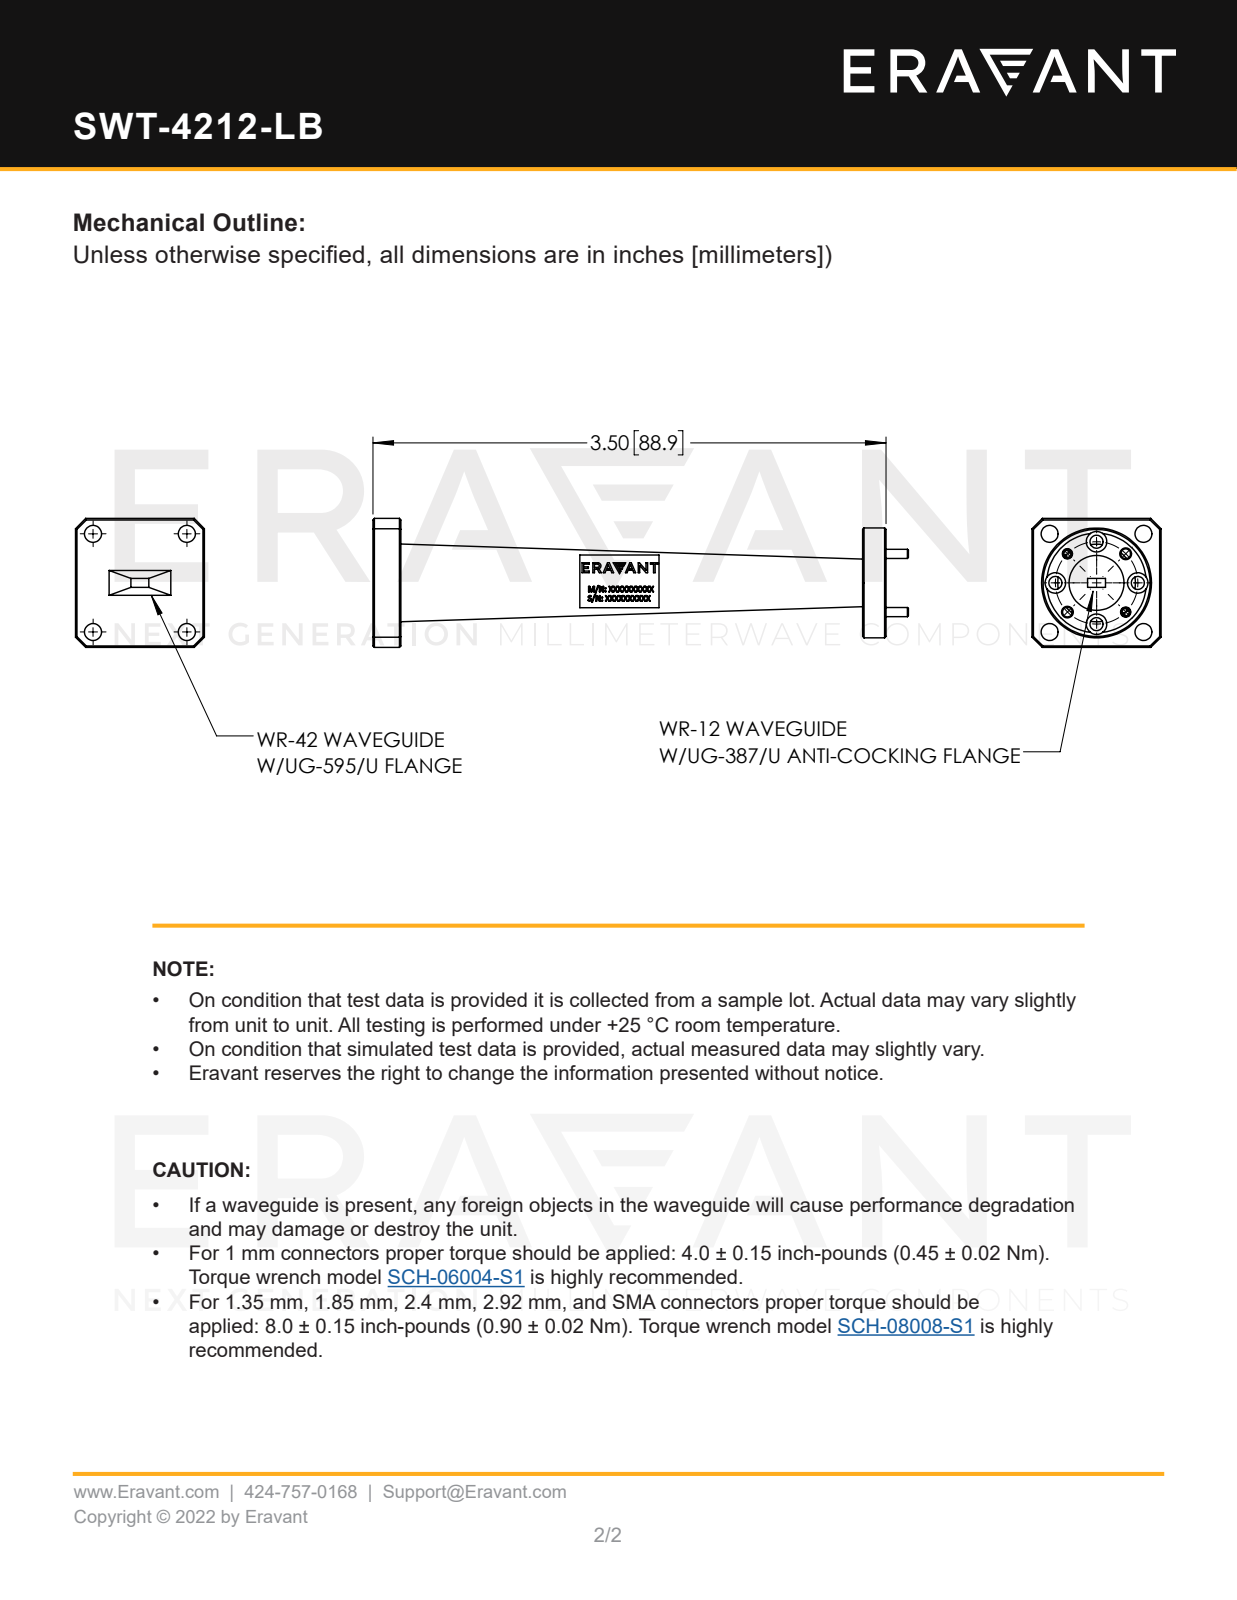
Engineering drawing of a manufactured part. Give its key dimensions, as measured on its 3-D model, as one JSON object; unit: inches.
{"part_name": "WT-KE, Defeatured", "step_written_by": "SolidWorks 2021 (AUTOMOTIVE_DESIGN)", "units": "inches", "bodies": {"solids": 3, "faces": 114, "planar": 48, "cylindrical": 44, "other": 22}, "overall_size": [3.652, 0.88, 0.88], "volume_in3": 0.708, "surface_area_in2": 8.132, "round_holes": [[0.089, 4], [0.116, 4], [0.14, 4], [0.061, 2], [0.067, 2], [0.68, 1]], "round_bosses_or_shafts": [[0.063, 2], [0.75, 1], [0.375, 1]], "face_to_face_distances": [0.19, 3.34, 3.15, 0.88, 3.48, 3.29, 0.14, 3.5, 3.31, 0.16], "hole_center_spacings": [0.215, 0.281, 0.398, 0.519, 0.182, 0.324, 0.337, 0.463]}
